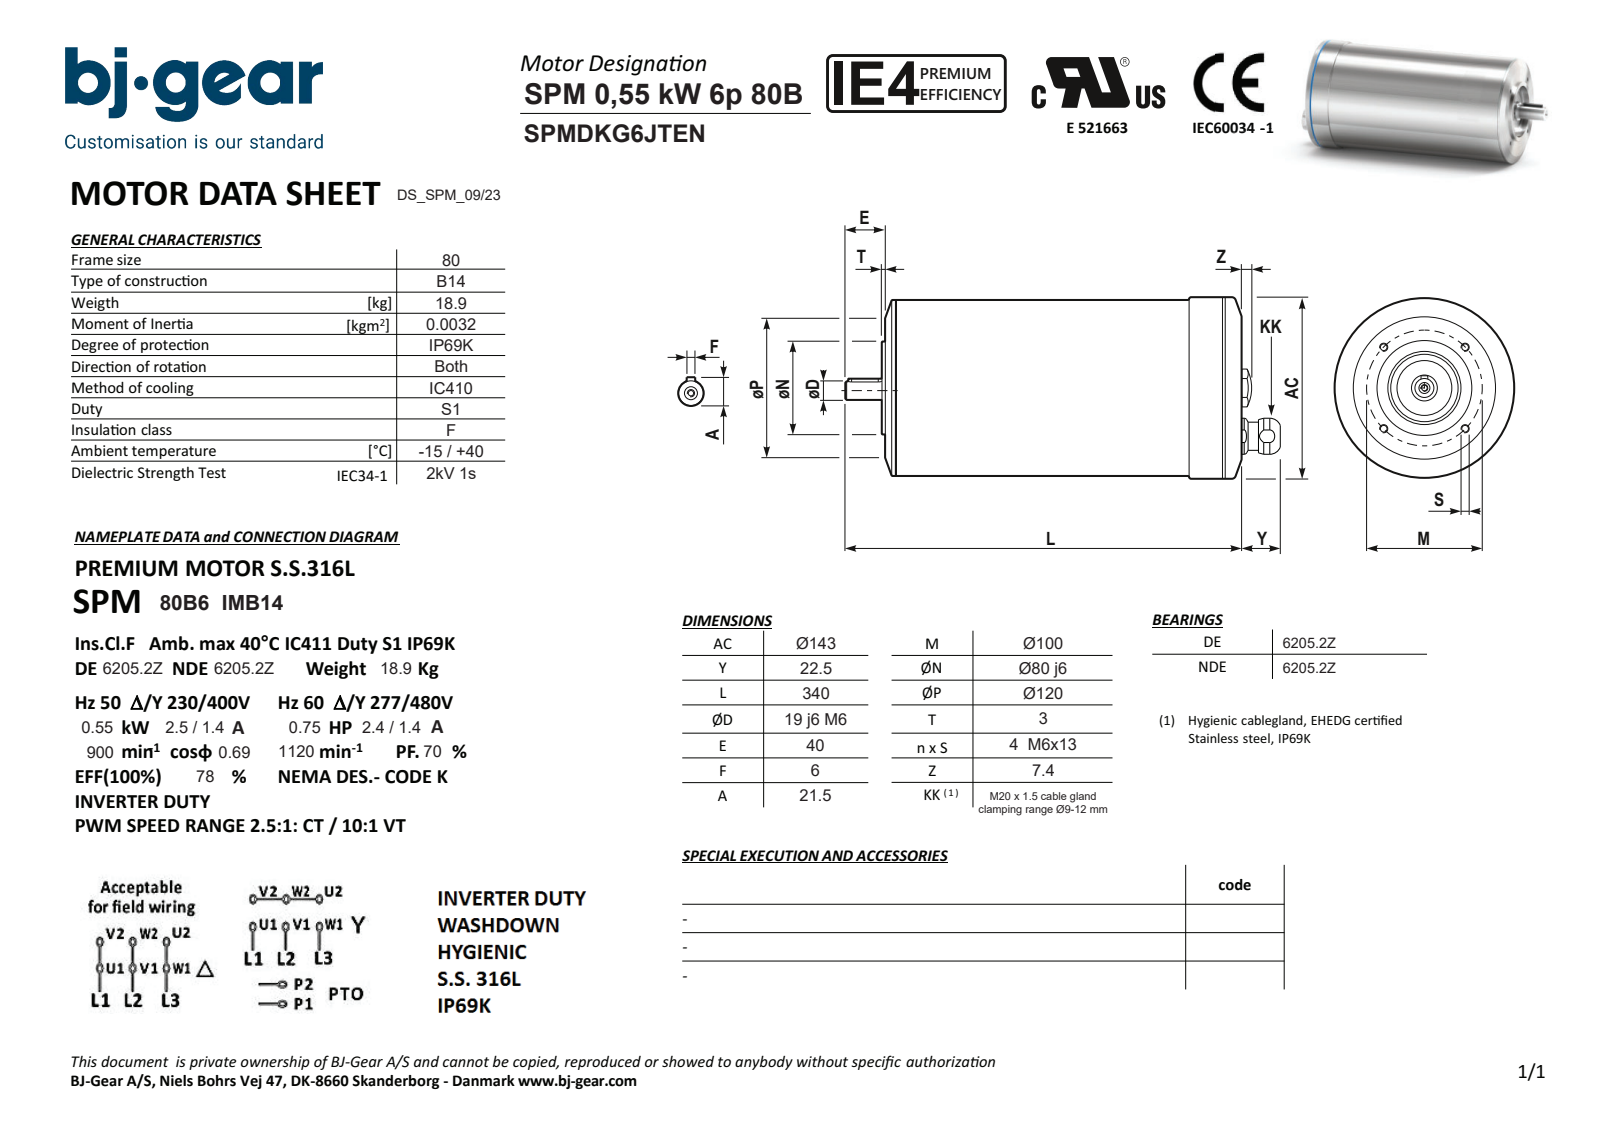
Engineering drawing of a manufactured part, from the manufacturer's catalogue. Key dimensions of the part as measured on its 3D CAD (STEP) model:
Part name (STEP PRODUCT): SPMDKG6JTENN4KSA1-N---NNN
STEP written by: Solid Edge (AUTOMOTIVE_DESIGN)
Units: millimetres
Bodies: 1 solid, 87 faces (30 planar, 32 cylindrical, 25 other)
Overall size (bounding box): 367.5 × 143 × 143
Volume: 4 570 000 mm³ · Surface area: 168 444 mm²
Round holes (diameter × count): ⌀4.92 ×5, ⌀6.4 ×1, ⌀7 ×1, ⌀13.4 ×1, ⌀68 ×1
Round bosses / shafts (diameter × count): ⌀143 ×1, ⌀142.98 ×1, ⌀139 ×1, ⌀138.98 ×1, ⌀80 ×1, ⌀25 ×1, ⌀20 ×1, ⌀19 ×1
Partial cylindrical surfaces — rounded edges, fillets, slot ends (radius × count): R3 ×2, R12.8 ×1
Main face-to-face distances: 300, 6, 294, 9, 303, 3, 24, 340, 46, 40
Hole centre spacings: 50.01, 70.72, 35.46, 81.44, 100.01, 38
